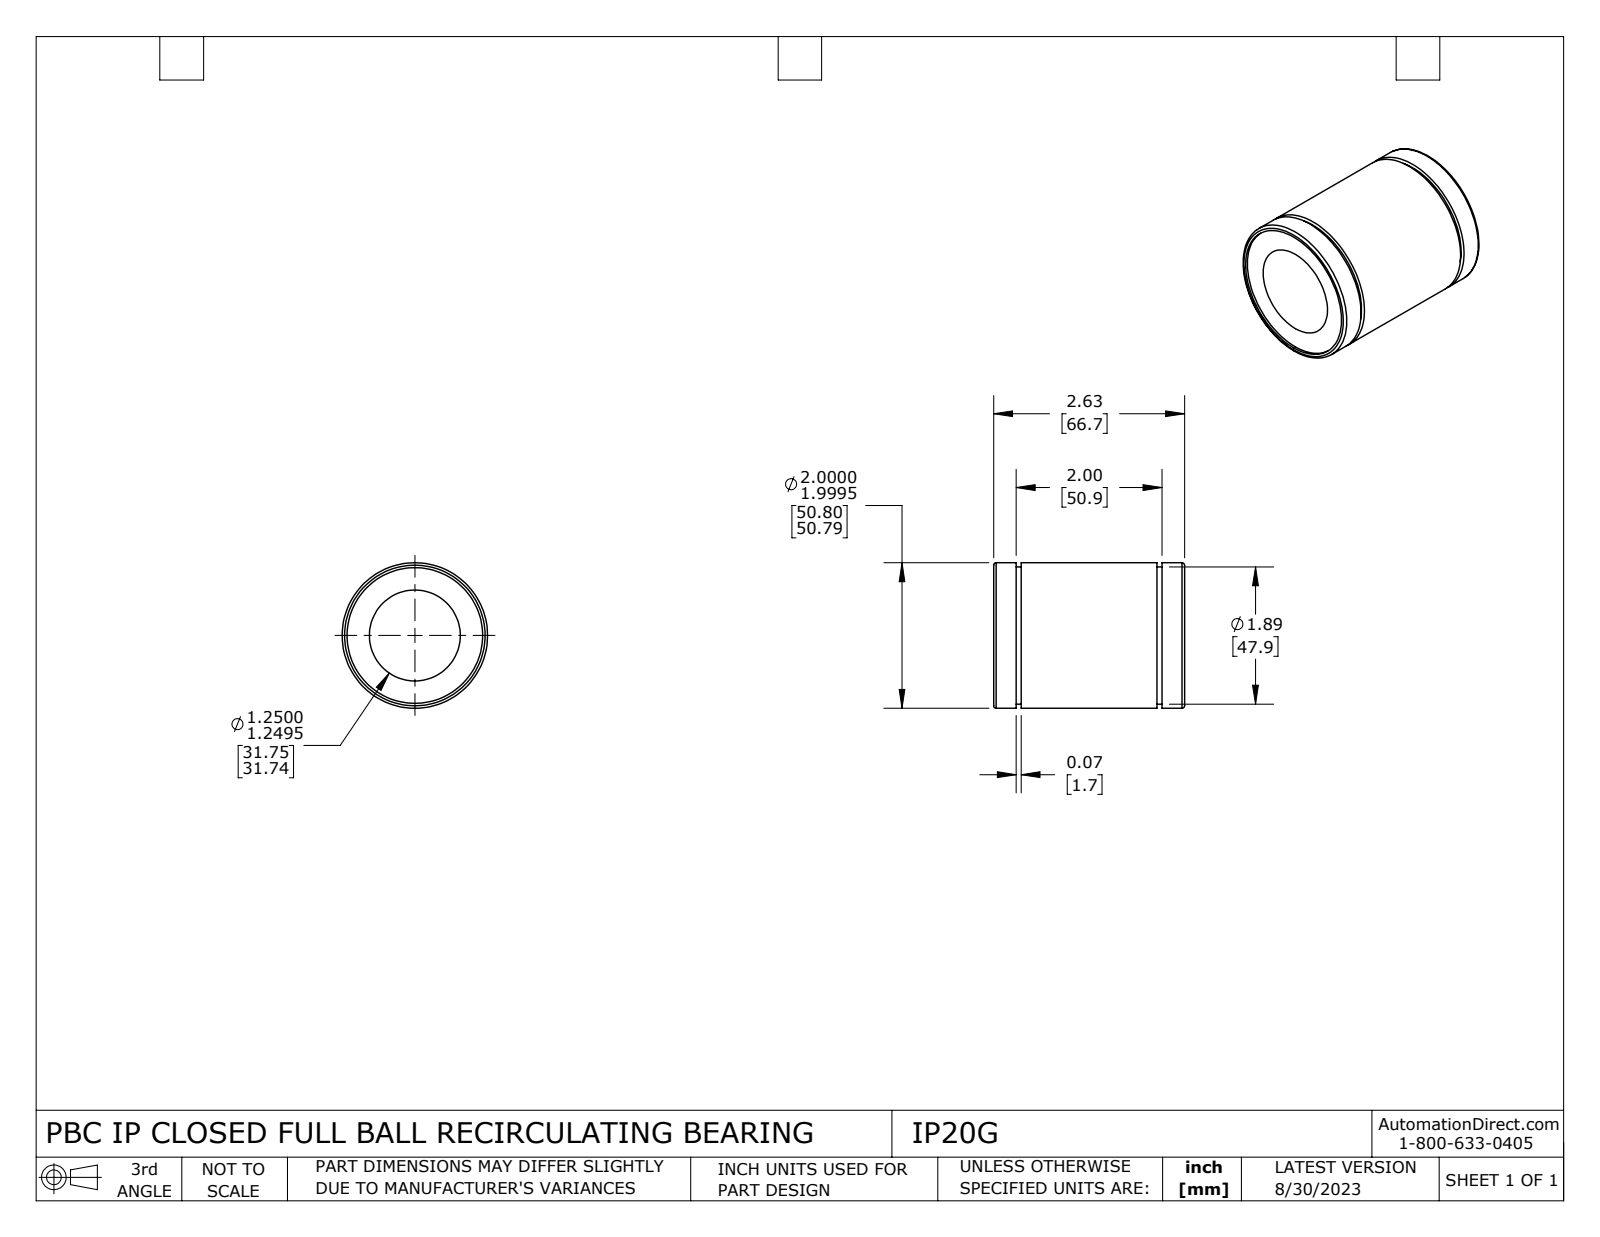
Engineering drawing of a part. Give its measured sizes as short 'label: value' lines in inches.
name: IP20G
written by: SolidWorks 2021 (CONFIG_CONTROL_DESIGN)
unit: in
bodies: 1 solid, 28 faces (8 planar, 16 cylindrical, 4 other)
size: 2.625 × 2 × 2
volume: 4.873 in³; area: 31.92 in²
holes: 1× ⌀1.25, 1× ⌀1.864
bosses: 1× ⌀2, 1× ⌀1.886
face distances: 2.557, 0.276, 0.344, 2.213, 2.281, 1.937, 0.068, 0.034, 0.31, 0.378
